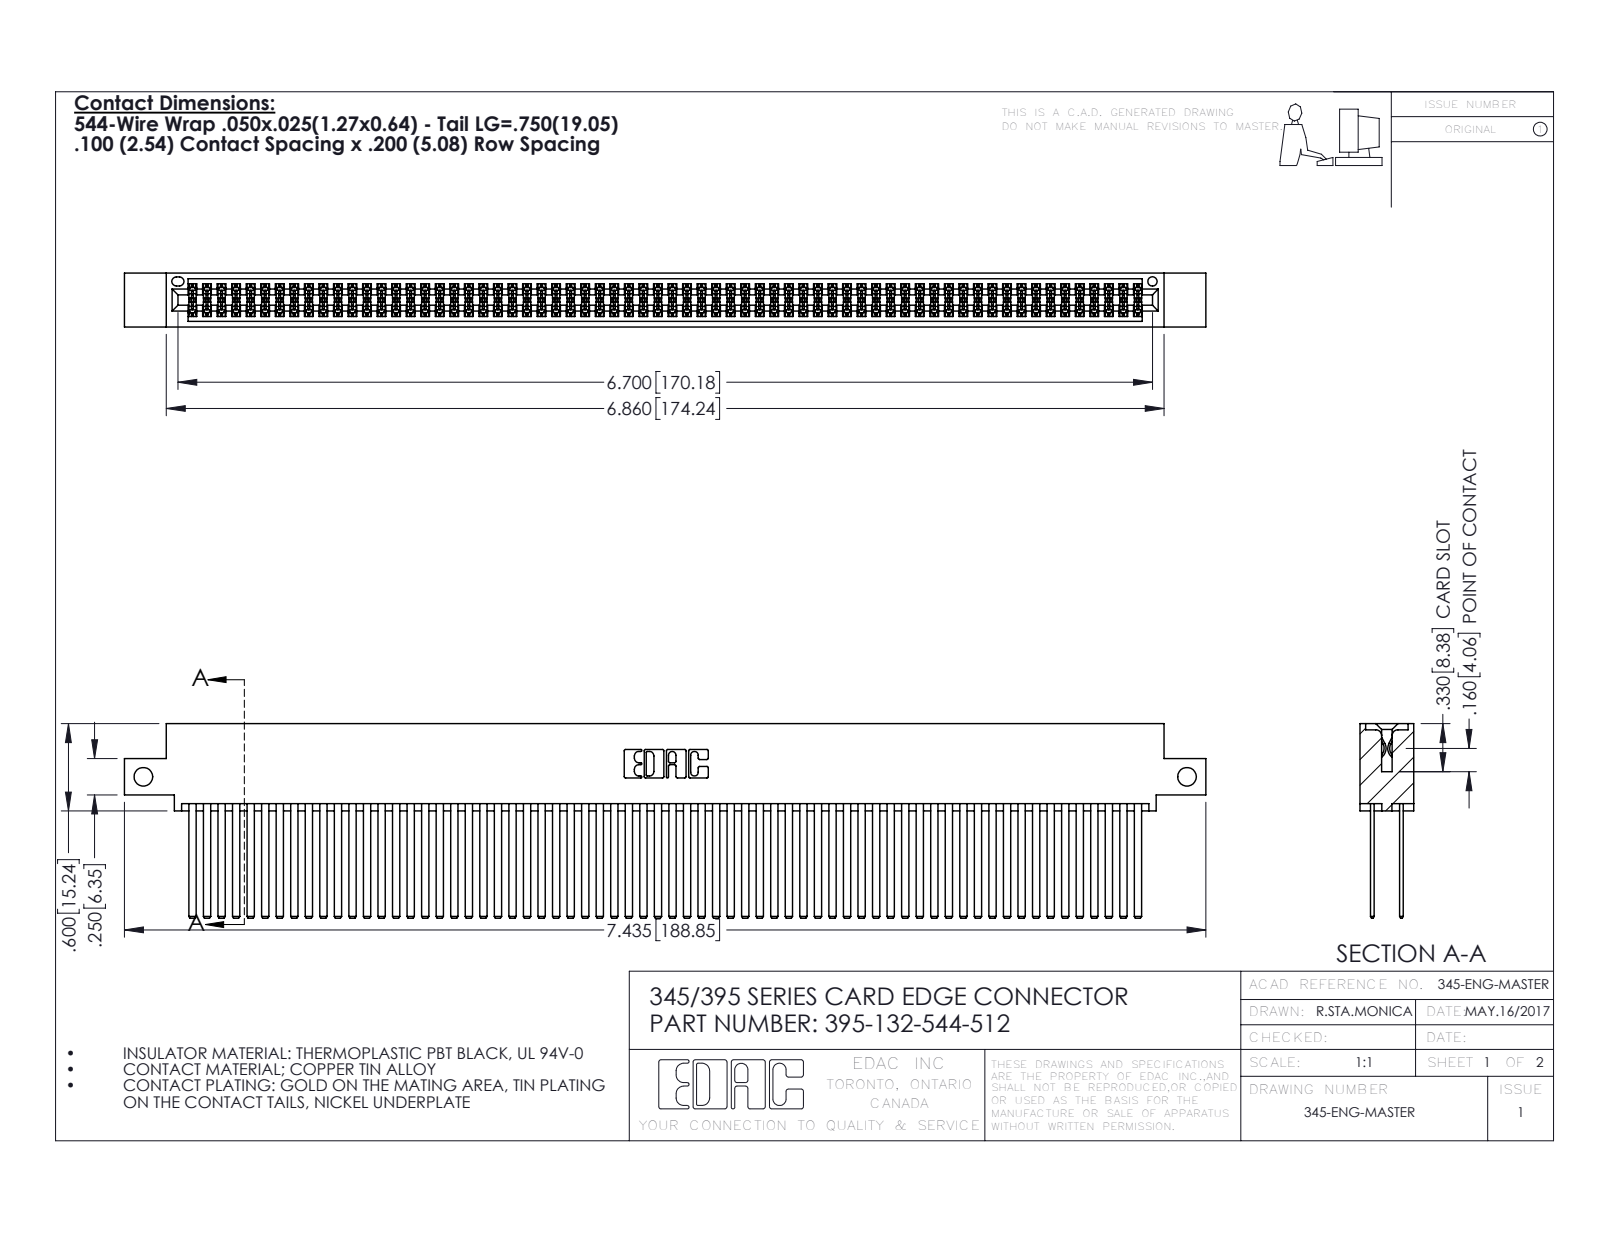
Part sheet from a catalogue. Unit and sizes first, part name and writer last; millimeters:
Units: millimetres
Overall size (bounding box): 188.8 × 34 × 9.4
Round holes (diameter × count): ⌀3.3 ×2, ⌀1.6 ×1
Partial cylindrical surfaces — rounded edges, fillets, slot ends (radius × count): R0.2 ×198, R0.3 ×22, R0.2 ×6, R0.8 ×6, R0.7 ×3, R0.4 ×2, R0.5 ×2, R0.6 ×2
Main face-to-face distances: 5.1, 0.6, 7.6, 1.8, 2.5, 6.9, 5.7, 4.4, 9.4, 3.8
Hole centre spacings: 182.2
Volume: 20 250 mm³ · Surface area: 35 790 mm²
Bodies: 133 solids, 5938 faces (3912 planar, 2026 cylindrical, 0 other)
Part name (STEP PRODUCT): 395-132-544-512; 345-292-001_345-293-144; 345 Part_0.110 Offset - Side Mount
STEP written by: SolidWorks 2016 (CONFIG_CONTROL_DESIGN)
